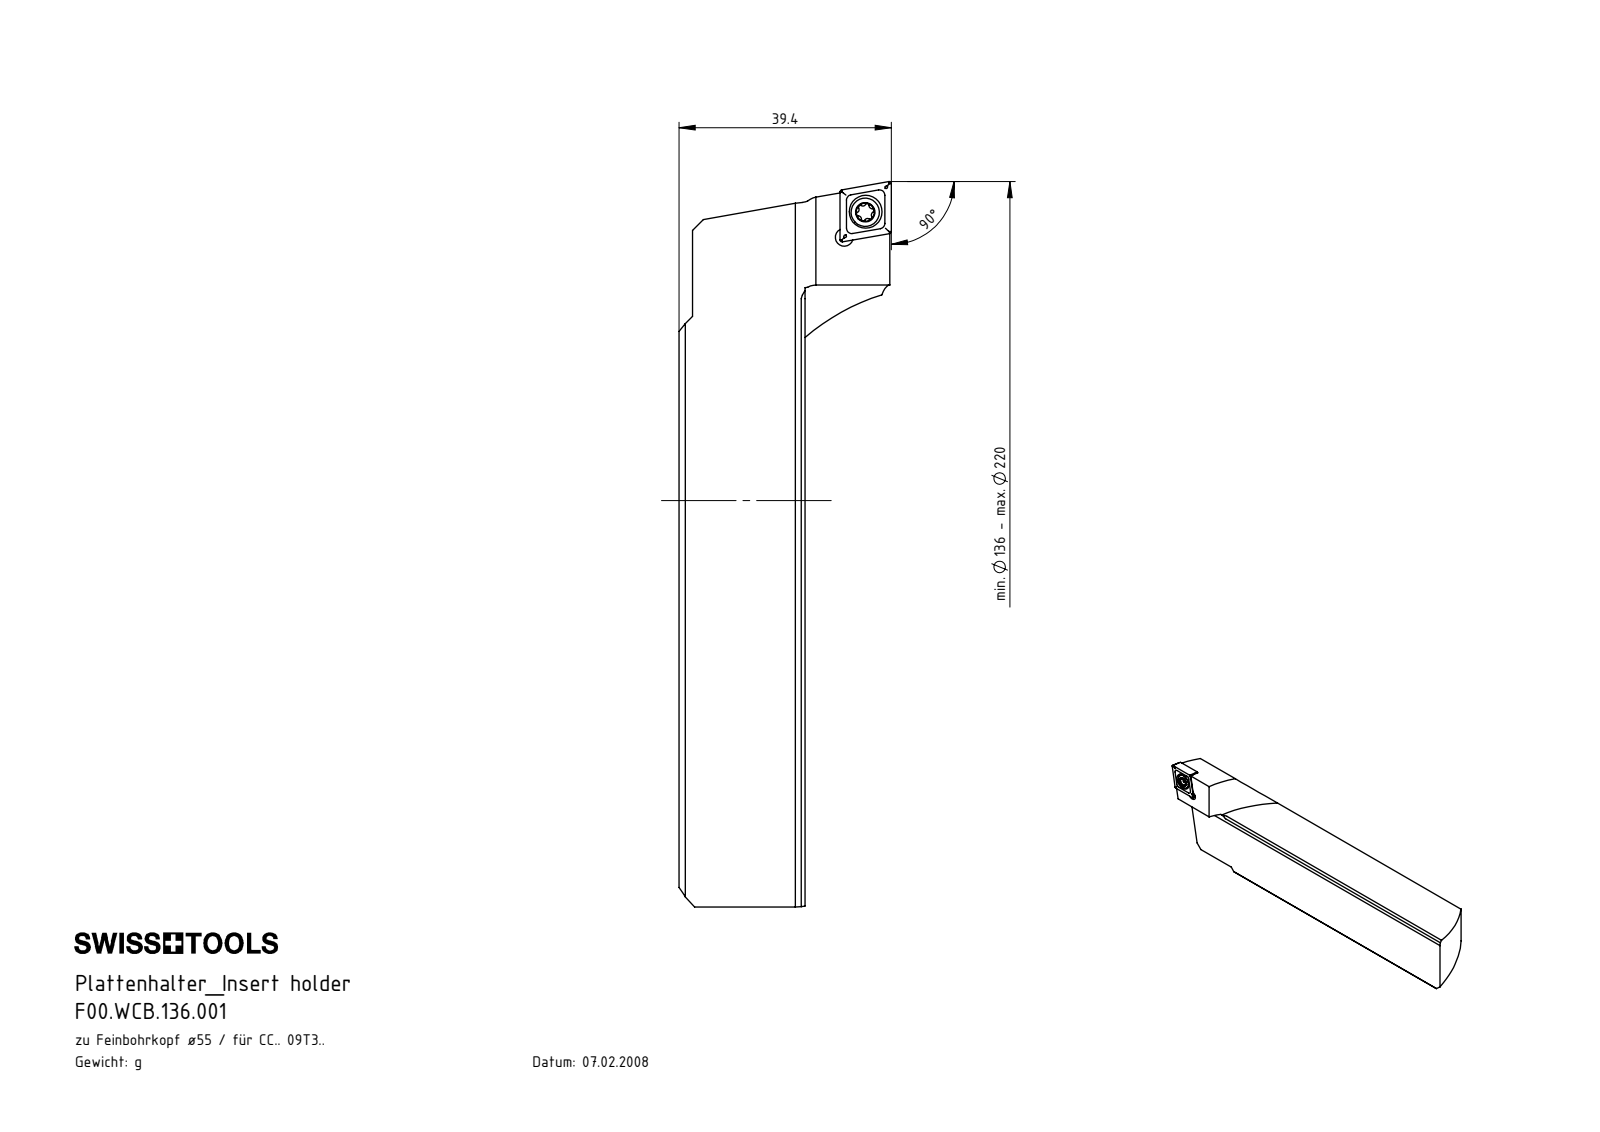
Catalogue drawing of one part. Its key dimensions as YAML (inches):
part_name: "CCMT09T304; F00.WCB.136.001; F00-WCB.136.001_C; WCB-ER2.001.009_A"
step_written_by: "SolidWorks 2017 (AUTOMOTIVE_DESIGN)"
units: inches
bodies: {solids: 3, faces: 559, planar: 342, cylindrical: 39, other: 178}
overall_size: [5.298, 1.551, 1.077]
volume: 3.396
surface_area: 21.7
round_holes:
  - {diameter: 0.13, count: 2}
  - {diameter: 0.173, count: 1}
  - {diameter: 0.24, count: 1}
round_bosses_or_shafts:
  - {diameter: 0.207, count: 1}
  - {diameter: 0.157, count: 1}
partial_cylinders:
  - {radius: 0.008, count: 8}
  - {radius: 0.013, count: 6}
  - {radius: 0.023, count: 6}
  - {radius: 1.575, count: 3}
  - {radius: 0.031, count: 1}
face_to_face_distances: [0.094, 0.839, 0.187, 0.281, 0.375, 0.188, 0.281, 0.375, 0.469, 0.563]
hole_center_spacings: [0.239, 0.244]
